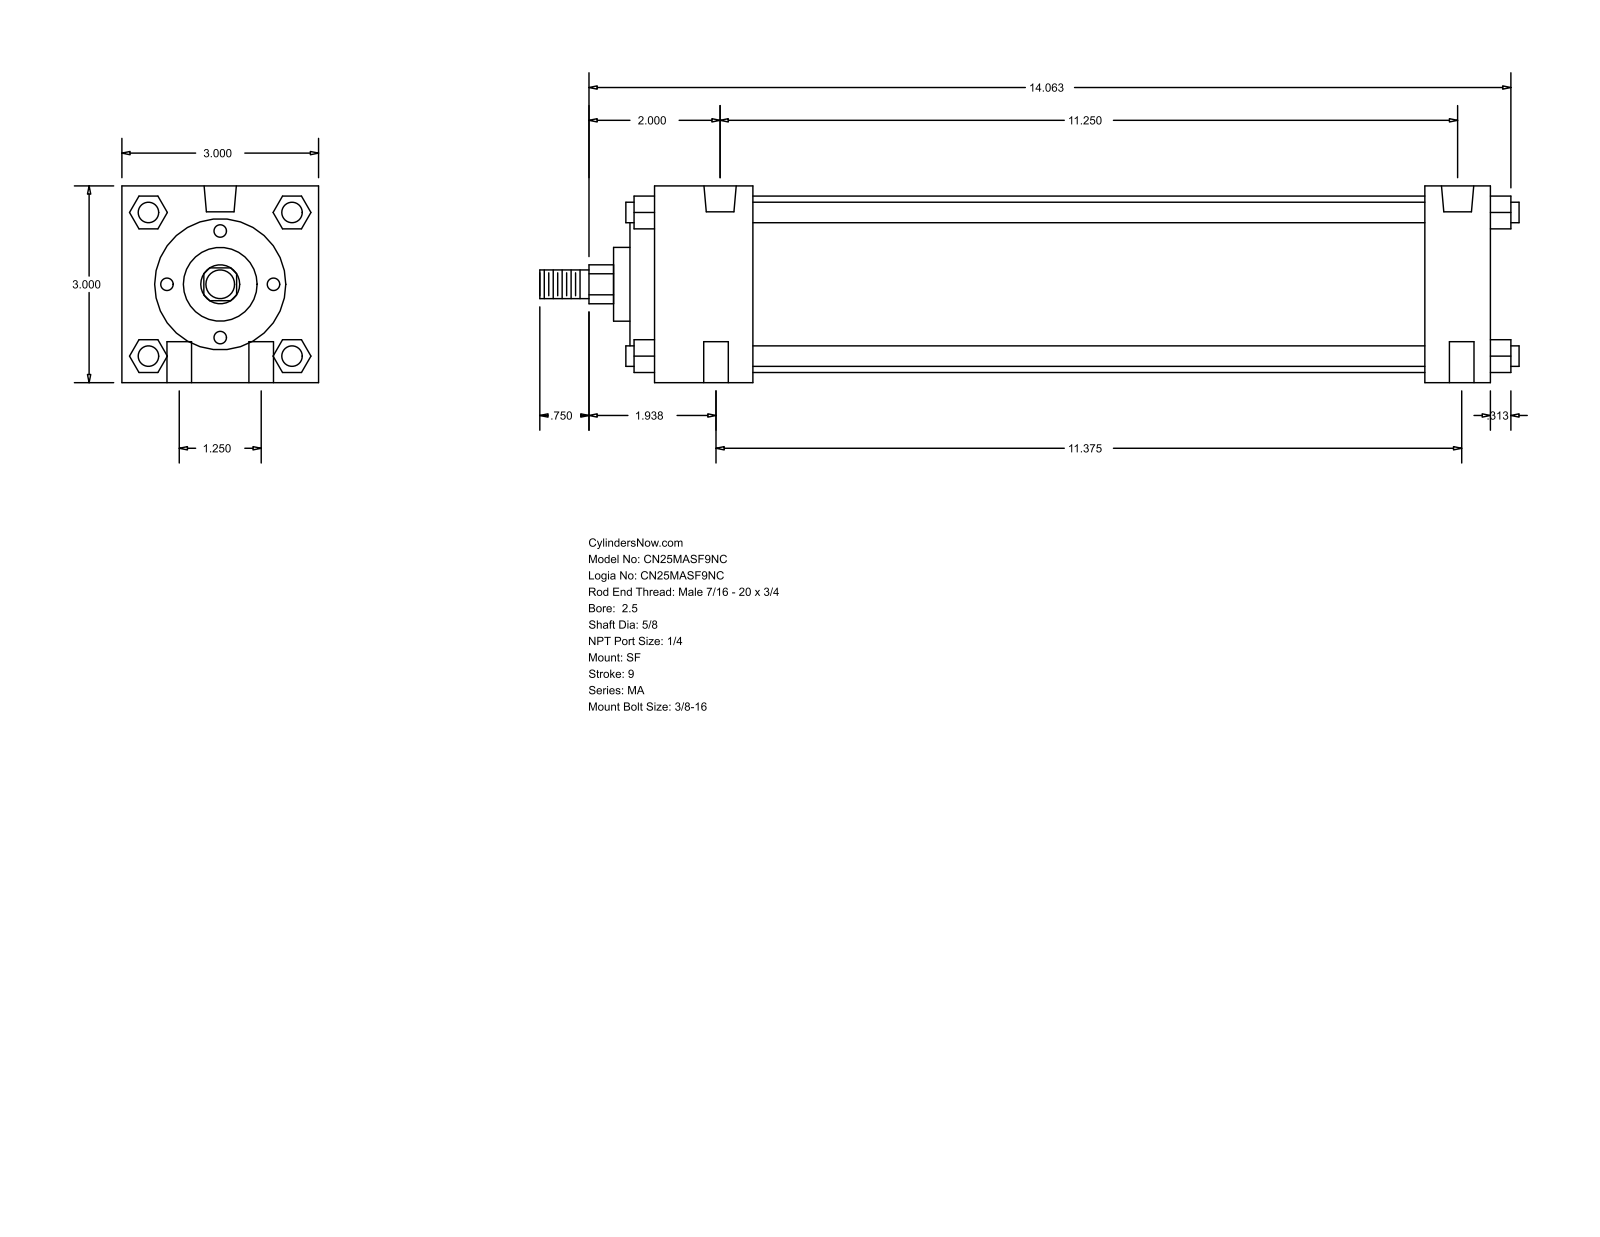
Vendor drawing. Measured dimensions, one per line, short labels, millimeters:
name: MA_SF__0250_0.625
written by: GSSL Pune (CONFIG_CONTROL_DESIGN)
unit: mm
bodies: 0 solids, 126 faces (95 planar, 31 cylindrical, 0 other)
size: 379.41 × 76.2 × 76.2
holes: 4× ⌀9.53, 2× ⌀7.94, 2× ⌀12.49
bosses: 4× ⌀7.94, 1× ⌀68.33, 1× ⌀50.8, 1× ⌀28.57, 1× ⌀15.88, 1× ⌀11.11
rounds: 1× R7.54
face distances: 76.2, 323.85, 25.4, 298.45, 38.1, 260.35, 285.75, 12.7, 9.52, 47.62
hole spacings: 15.96, 287.78, 31.76, 285.75, 288.93, 290.67
